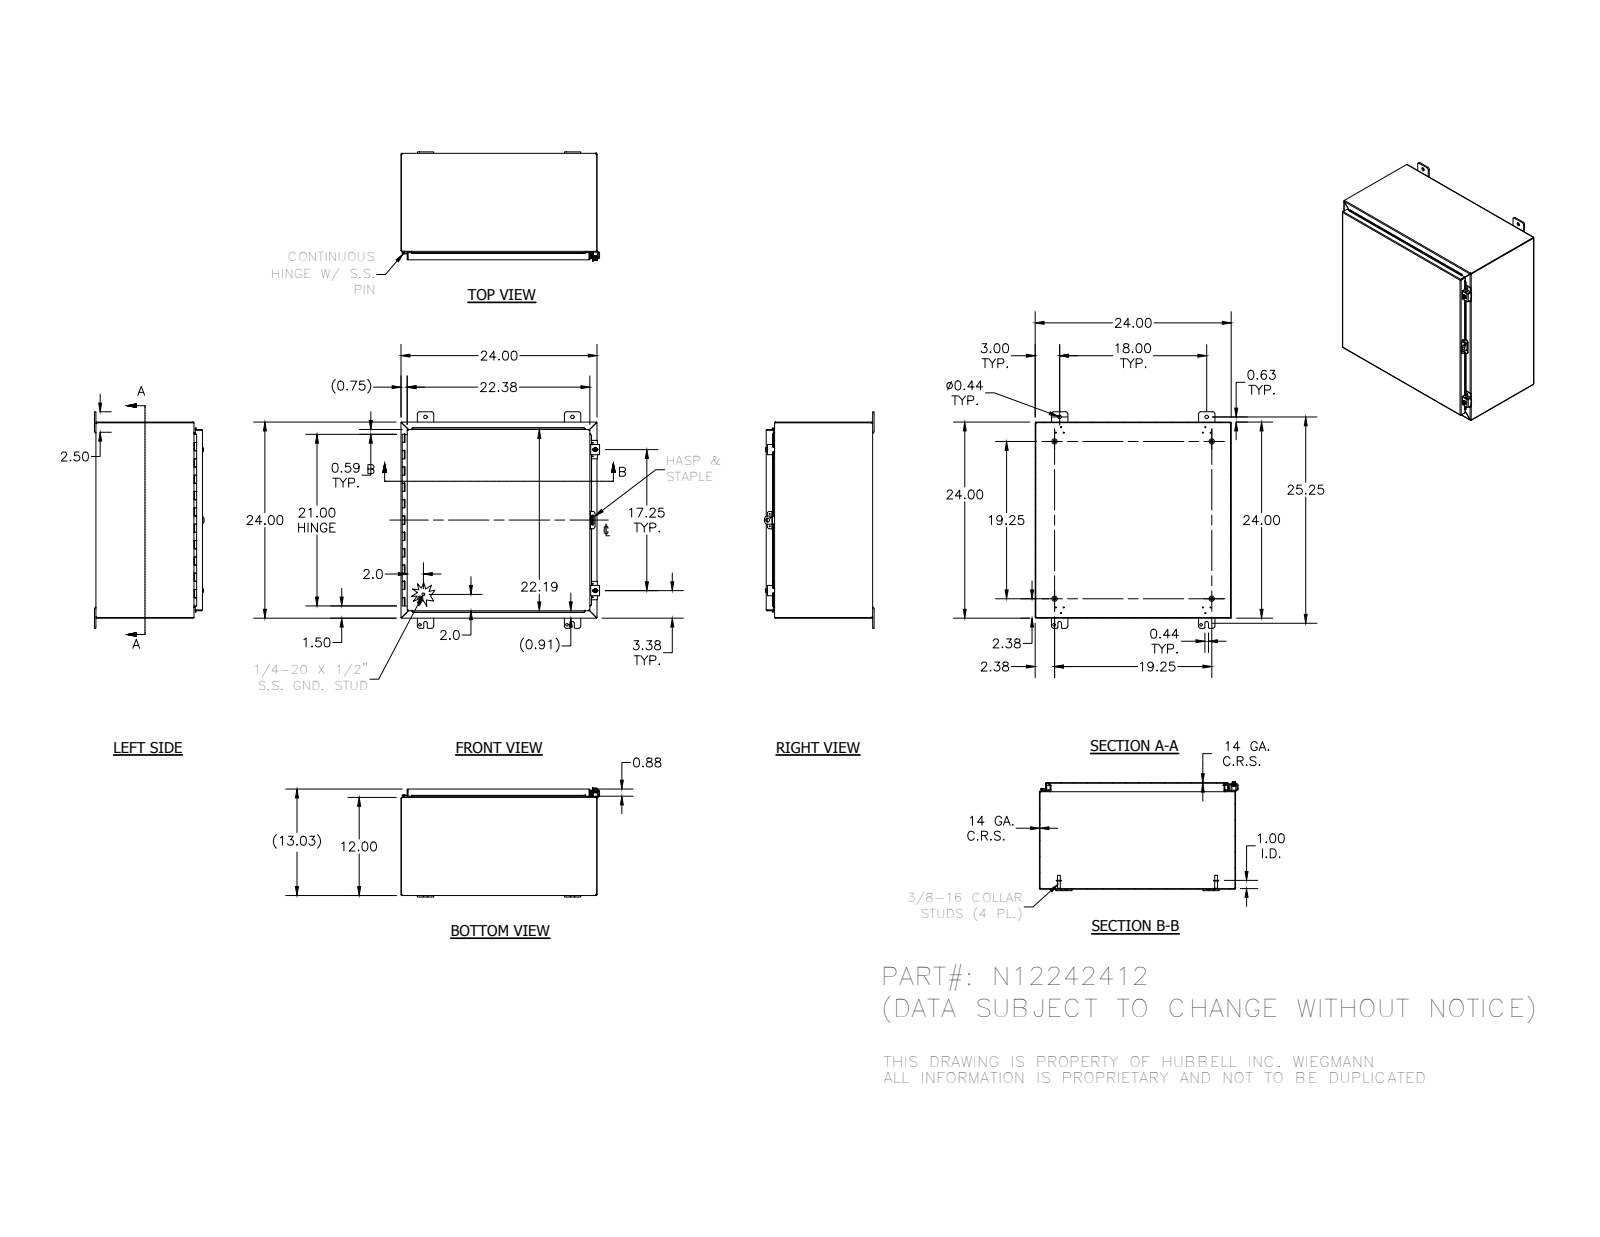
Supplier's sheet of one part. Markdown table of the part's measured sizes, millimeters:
| quantity | value |
| --- | --- |
| part name | N12242412; 34840; 38420; N12242412BKP (+8 more) |
| STEP written by | Autodesk Inventor 2012 (AUTOMOTIVE_DESIGN) |
| units | millimeters |
| bodies | 27 solids, 982 faces (533 planar, 332 cylindrical, 117 other) |
| overall size | 673.1 × 617.5 × 340.6 |
| volume | 3 305 000 mm³ |
| surface area | 3 418 000 mm² |
| round holes (diameter × count) | 3 × 12, 2.8 × 7, 8 × 4, 11.1 × 4, 5.4 × 2, 7.1 × 2, 7.6 × 2, 3.2 × 1, 4 × 1, 12.7 × 1 |
| round bosses / shafts (diameter × count) | 15.9 × 4, 8.4 × 4, 6.4 × 4, 13.2 × 2, 12.7 × 2, 8.9 × 2, 2.9 × 2, 8.6 × 1 |
| partial cylindrical surfaces (radius × count) | 0.8 × 27, 1.6 × 25, 3.2 × 25, 6.4 × 25, 0.8 × 23, 2.7 × 23, 1.8 × 8, 2.5 × 4 |
| main face-to-face distances | 1.9, 607.7, 329.2, 609.6, 605.8, 327.3, 331, 302.9, 26.2, 304.8 |
| hole center spacings | 457.2, 19.3, 23.9, 24.6, 441.2, 465.8, 543.1, 543.6 |
